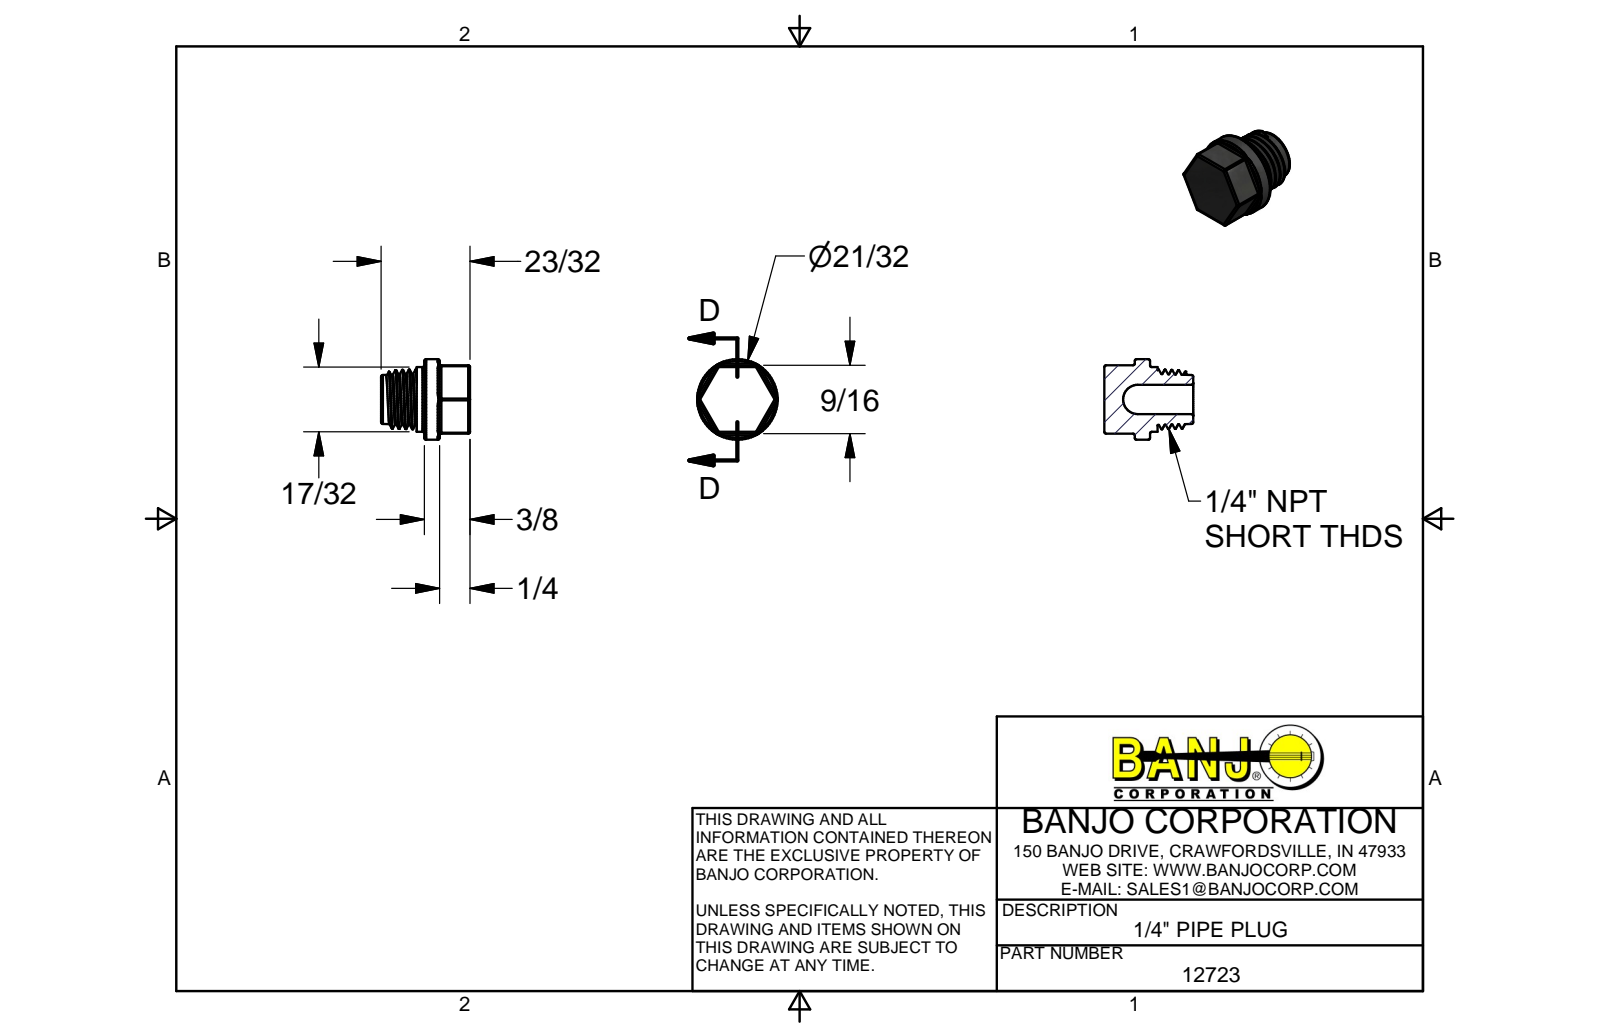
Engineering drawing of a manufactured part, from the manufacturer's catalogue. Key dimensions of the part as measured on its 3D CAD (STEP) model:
Part name (STEP PRODUCT): 12723
STEP written by: Autodesk Inventor 2013 (AUTOMOTIVE_DESIGN)
Units: inches
Bodies: 1 solid, 113 faces (17 planar, 33 cylindrical, 63 other)
Overall size (bounding box): 0.73 × 0.66 × 0.66
Volume: 0.144 in³ · Surface area: 2.451 in²
Round holes (diameter × count): ⌀0.24 ×1
Round bosses / shafts (diameter × count): ⌀0.66 ×1, ⌀0.53 ×1
Partial cylindrical surfaces — rounded edges, fillets, slot ends (radius × count): R0.015 ×18
Main face-to-face distances: 0.56, 0.375, 0.437, 0.062, 0.73, 0.355, 0.293, 0.25, 0.125, 0.187
